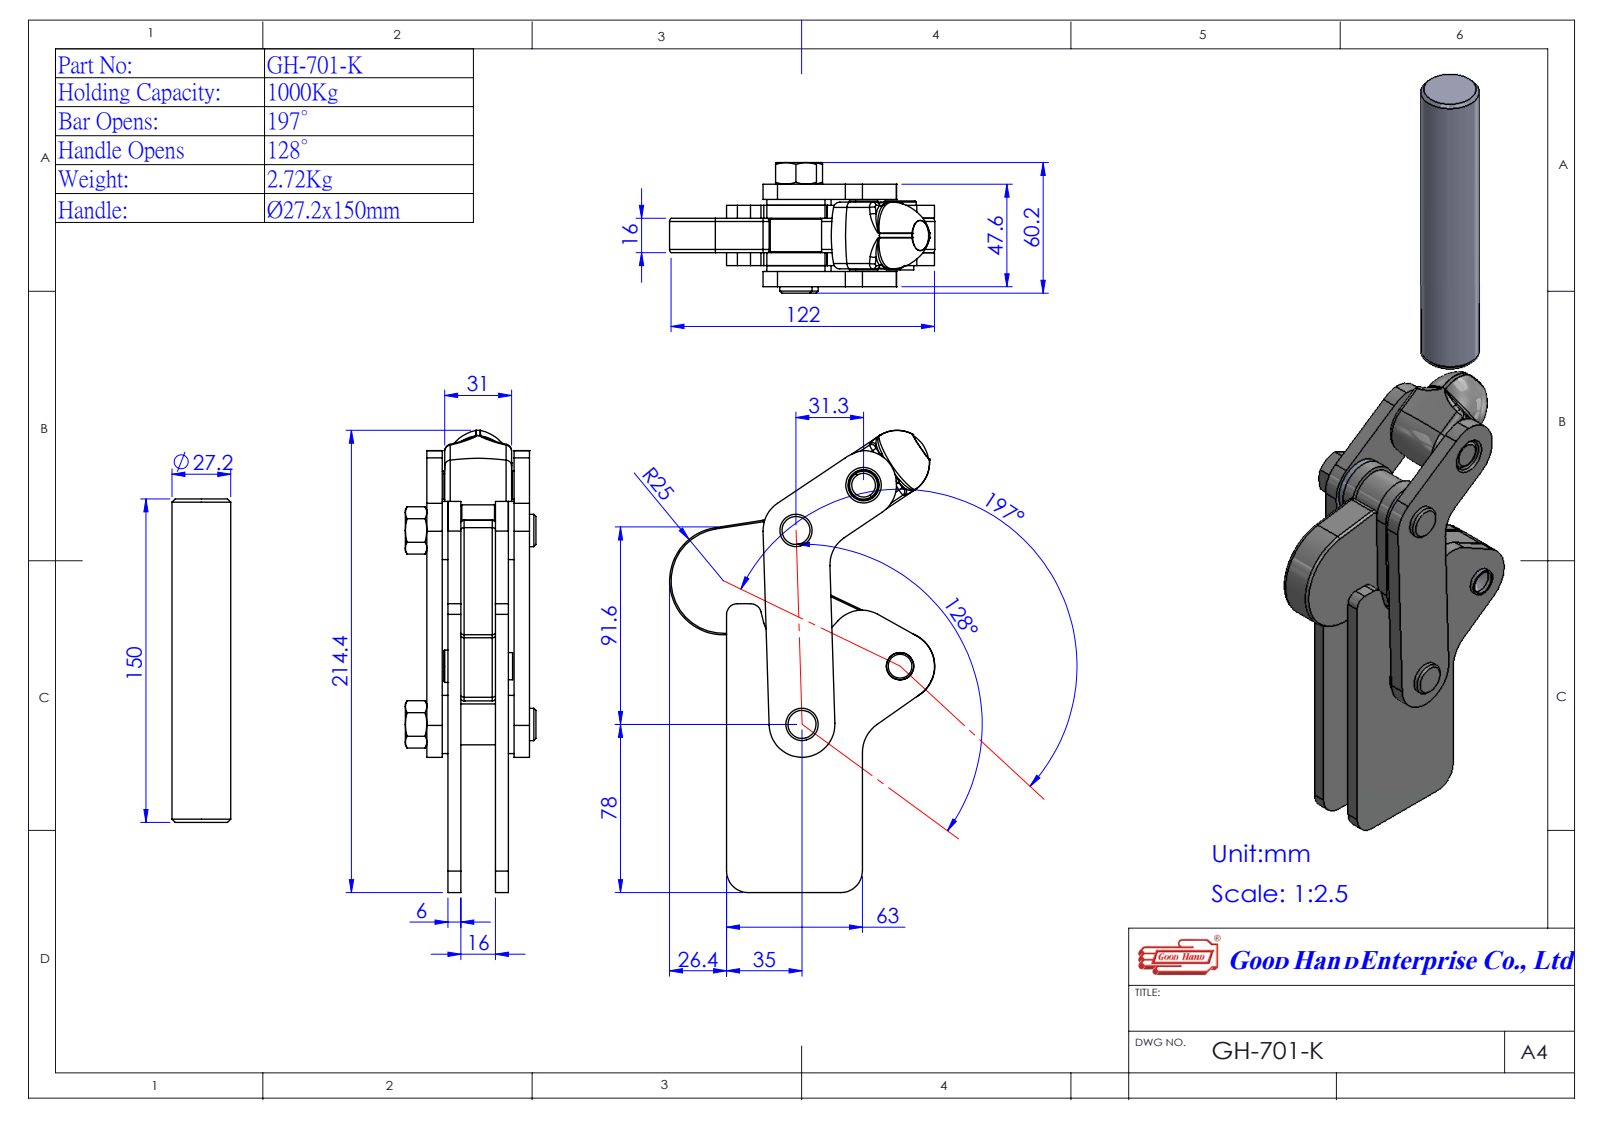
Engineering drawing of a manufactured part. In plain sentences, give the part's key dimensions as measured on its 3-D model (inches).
The part is named "Group6^GH-701-K(簡化)-1; GH-701-K(簡化)-1; 4702K152-1^GH-701-K(簡化)-1; 3701K26-1^GH-701-K(簡化)-1 (+3 more)". Its 3-D file was written by "SolidWorks 2016 (AUTOMOTIVE_DESIGN)". It is 6 solids with 257 faces: 95 planar, 109 cylindrical and 53 other. Overall it measures 14.437 by 4.832 by 2.488 inches. Its volume is 21.62 cubic inches and its surface area 197.1 square inches. Round holes: 3 of diameter 0.498, 1 of diameter 0.512, 1 of diameter 0.551, 1 of diameter 0.854. Round bosses or shafts: 4 of diameter 0.591, 3 of diameter 0.498, 2 of diameter 1.063, 2 of diameter 0.394, 1 of diameter 1.071, 1 of diameter 0.957. Partial cylindrical surfaces (rounded edges, fillets, slot ends): 4 of radius 0.591, 4 of radius 0.984, 3 of radius 0.63, 2 of radius 0.039, 2 of radius 0.197, 2 of radius 0.394, 2 of radius 3.209, 1 of radius 0.098. The main face-to-face distances are 0.236, 0.866, 0.63, 0.106, 0.343, 0.972, 1.209, 1.102, 0.28, 0.386. The hole center spacings are 1.46, 1.606, 1.946, 2.739, 3.55, 4.537.
